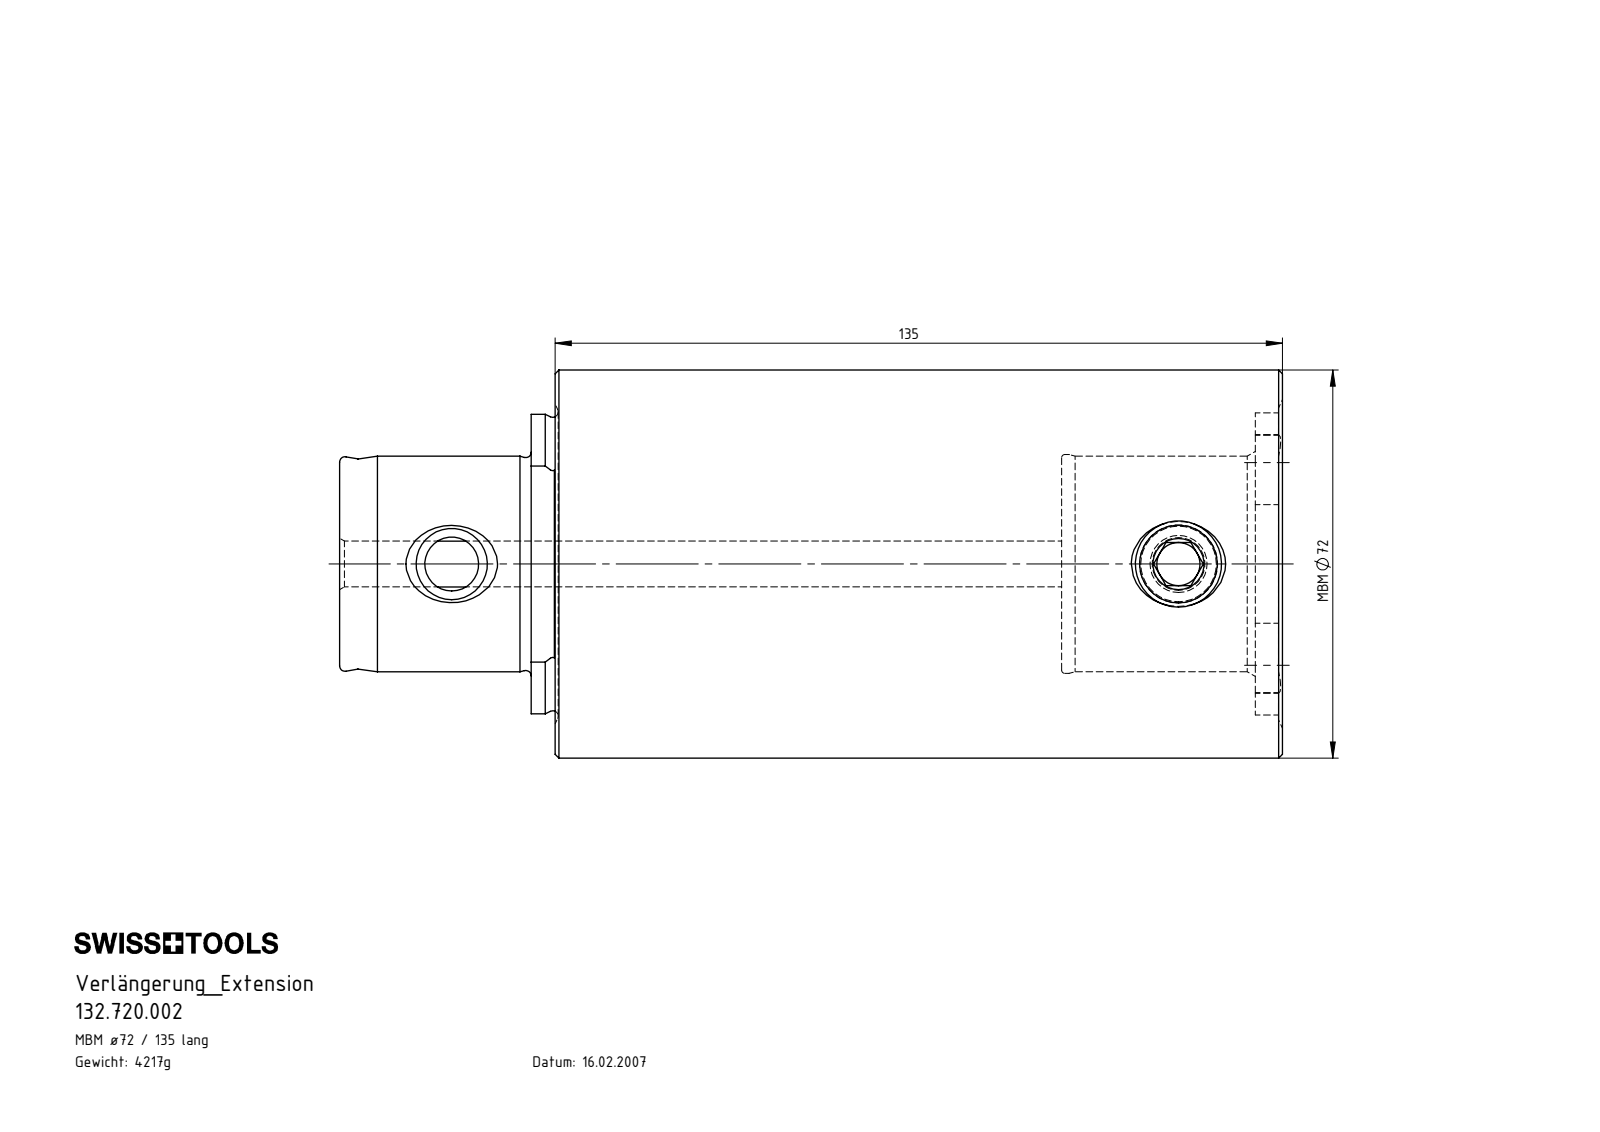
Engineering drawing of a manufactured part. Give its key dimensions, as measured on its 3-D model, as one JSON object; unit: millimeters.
{"part_name": "132.720.002; MB7-MB7.K01.135_C; MB7-ER1.001.022_A", "step_written_by": "SolidWorks 2017 (CONFIG_CONTROL_DESIGN)", "units": "millimeters", "bodies": {"solids": 2, "faces": 128, "planar": 34, "cylindrical": 33, "other": 61}, "overall_size": [175, 72, 72], "volume_mm3": 537250, "surface_area_mm2": 54696, "round_holes": [[8, 1], [8.5, 1], [10, 1], [14.5, 1], [40, 1], [40.6, 1]], "round_bosses_or_shafts": [[72, 1], [16, 1]], "partial_cylinders_radius": [[5.2, 4], [23.75, 1], [27.77, 1], [28.02, 1]], "face_to_face_distances": [94, 40, 134, 134.4, 175, 135, 41, 169.95, 129.95, 35.95], "hole_center_spacings": [134.9]}
